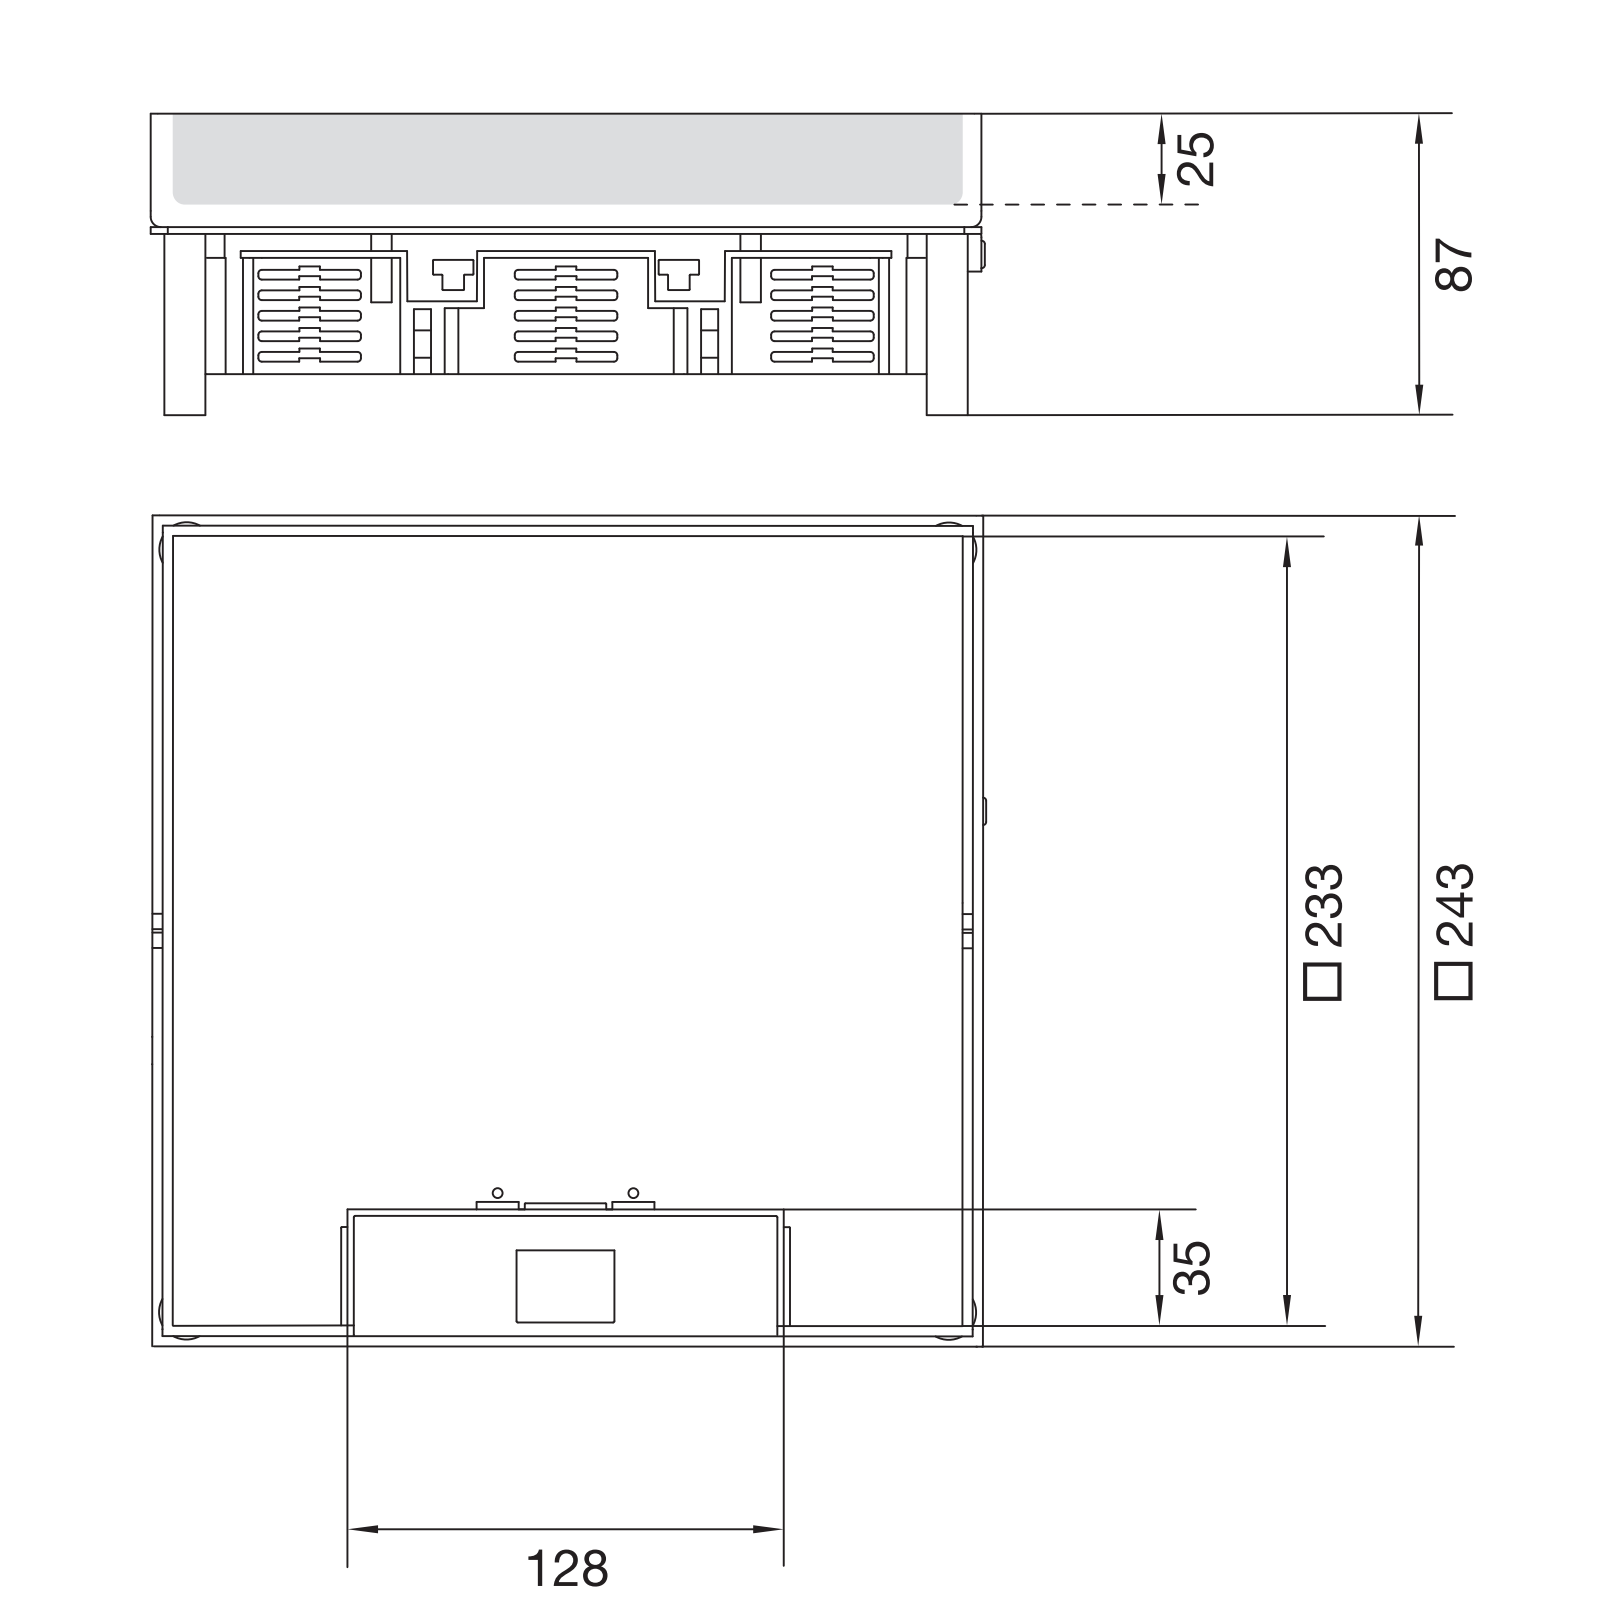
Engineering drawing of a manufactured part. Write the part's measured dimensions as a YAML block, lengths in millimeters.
part_name: "T-00731; T-00632; T-00625; T-00829_ASM (+7 more)"
step_written_by: "CREO PARAMETRIC BY PTC INC, 2022024 (AUTOMOTIVE_DESIGN)"
units: millimeters
bodies: {solids: 10, faces: 287, planar: 216, cylindrical: 63, other: 8}
overall_size: [243, 243, 87]
volume: 343872
surface_area: 337570
round_holes:
  - {diameter: 6.8, count: 4}
  - {diameter: 8.5, count: 4}
  - {diameter: 2.7, count: 2}
round_bosses_or_shafts:
  - {diameter: 12, count: 4}
  - {diameter: 9.85, count: 4}
partial_cylinders:
  - {radius: 1, count: 8}
  - {radius: 3, count: 8}
  - {radius: 6.6, count: 1}
  - {radius: 150, count: 1}
  - {radius: 152.5, count: 1}
face_to_face_distances: [2, 3, 2.5, 235, 5, 238, 6, 1, 241, 232]
hole_center_spacings: [223, 97.97, 136.08, 209.08, 229.43, 315.37, 40]
